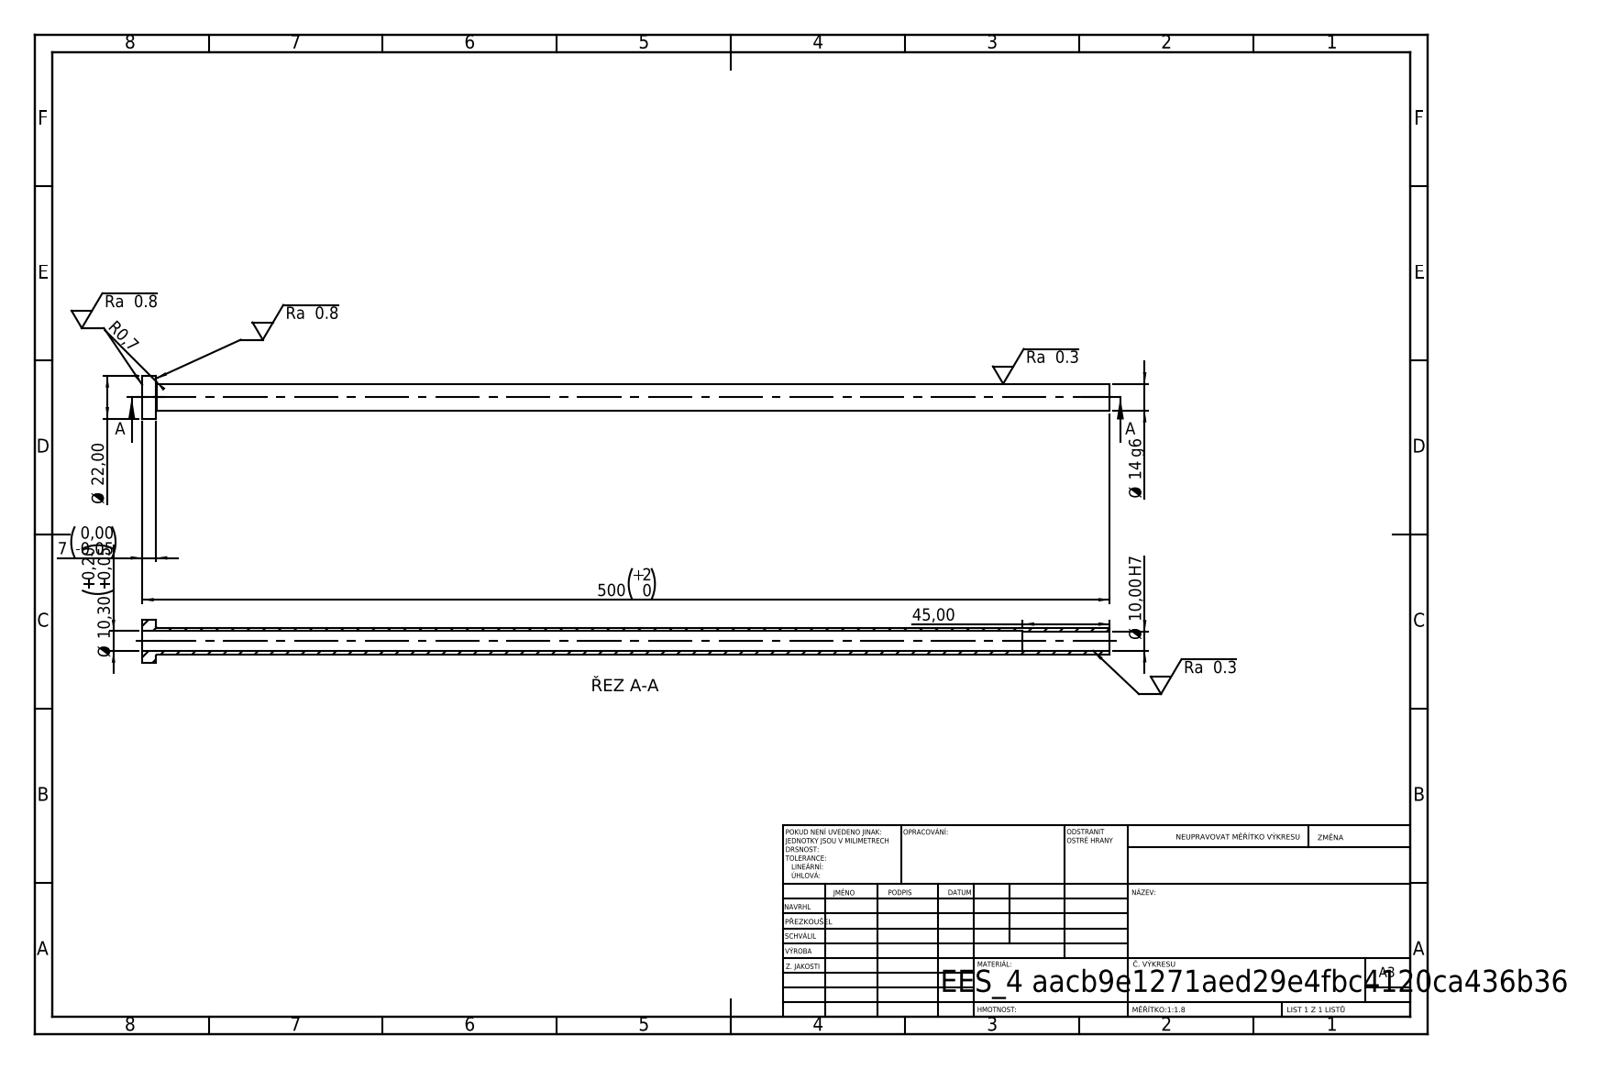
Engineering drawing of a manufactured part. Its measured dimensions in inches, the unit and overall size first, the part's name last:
Units: inches
Overall size (bounding box): 19.685 × 0.866 × 0.866
Round holes (diameter × count): ⌀0.394 ×1, ⌀0.406 ×1
Round bosses / shafts (diameter × count): ⌀0.866 ×1, ⌀0.551 ×1
Main face-to-face distances: 0.276, 19.685, 19.409, 17.913, 17.638, 1.772
Volume: 2.265 in³ · Surface area: 60.29 in²
Bodies: 1 solid, 14 faces (4 planar, 8 cylindrical, 2 other)
STEP written by: SolidWorks 2019 (CONFIG_CONTROL_DESIGN)
